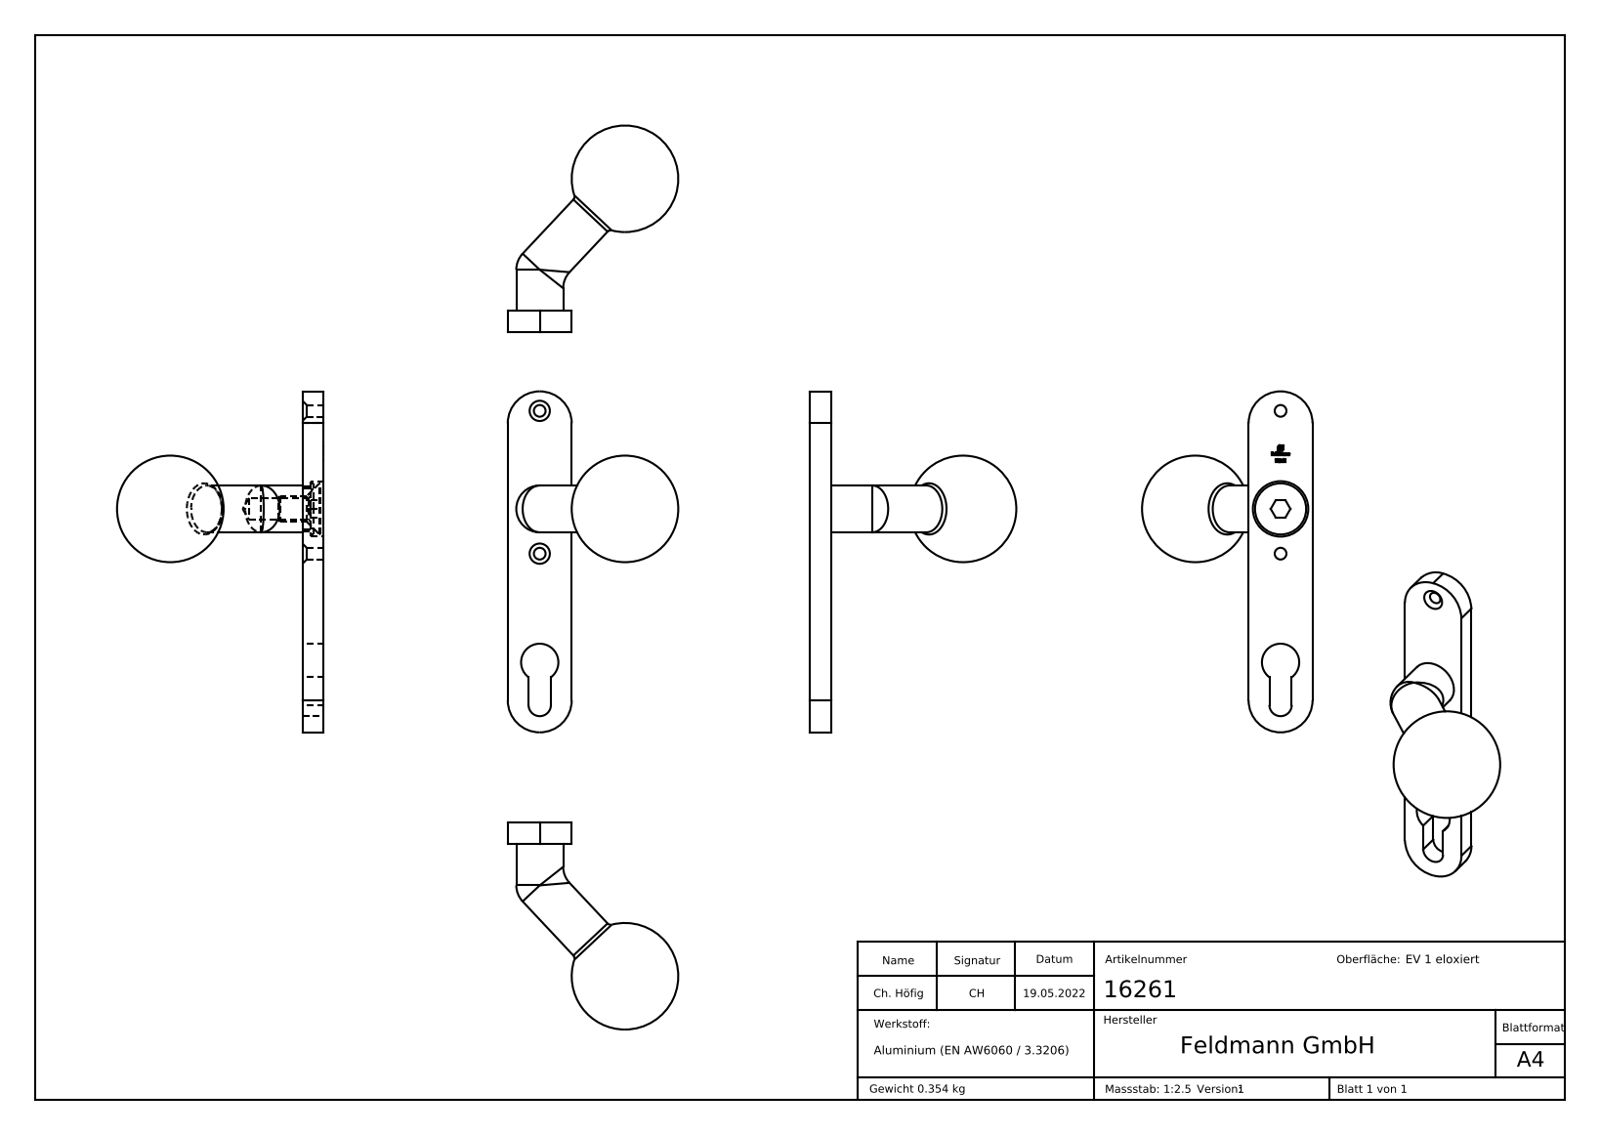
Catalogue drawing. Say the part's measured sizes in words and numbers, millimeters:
The part is named "16261 Teil1_16261 Teil1; DIN 7991 Konfig_M12x20; 16261; 16261 Teil2_16261 Teil2 (+1 more)". Its 3-D file was written by "SolidWorks 2018 (CONFIG_CONTROL_DESIGN)". It is 4 solids with 268 faces: 144 planar, 21 cylindrical and 103 other. Overall it measures 160 by 97 by 80 millimeters. Its volume is 124 848 cubic millimeters and its surface area 28 101 square millimeters. Round holes: 2 of diameter 5.5, 1 of diameter 10.2, 1 of diameter 17.5, 1 of diameter 18, 1 of diameter 21, 1 of diameter 26. Round bosses or shafts: 2 of diameter 22, 1 of diameter 24, 1 of diameter 23.5, 1 of diameter 19.75, 1 of diameter 12. Partial cylindrical surfaces (rounded edges, fillets, slot ends): 2 of radius 0.75, 2 of radius 15, 1 of radius 5.25. The main face-to-face distances are 10, 30, 4, 6, 1.5, 4.5, 8.5, 5, 9.75, 20.25. The hole center spacings are 21, 46, 51, 67, 72, 118.
